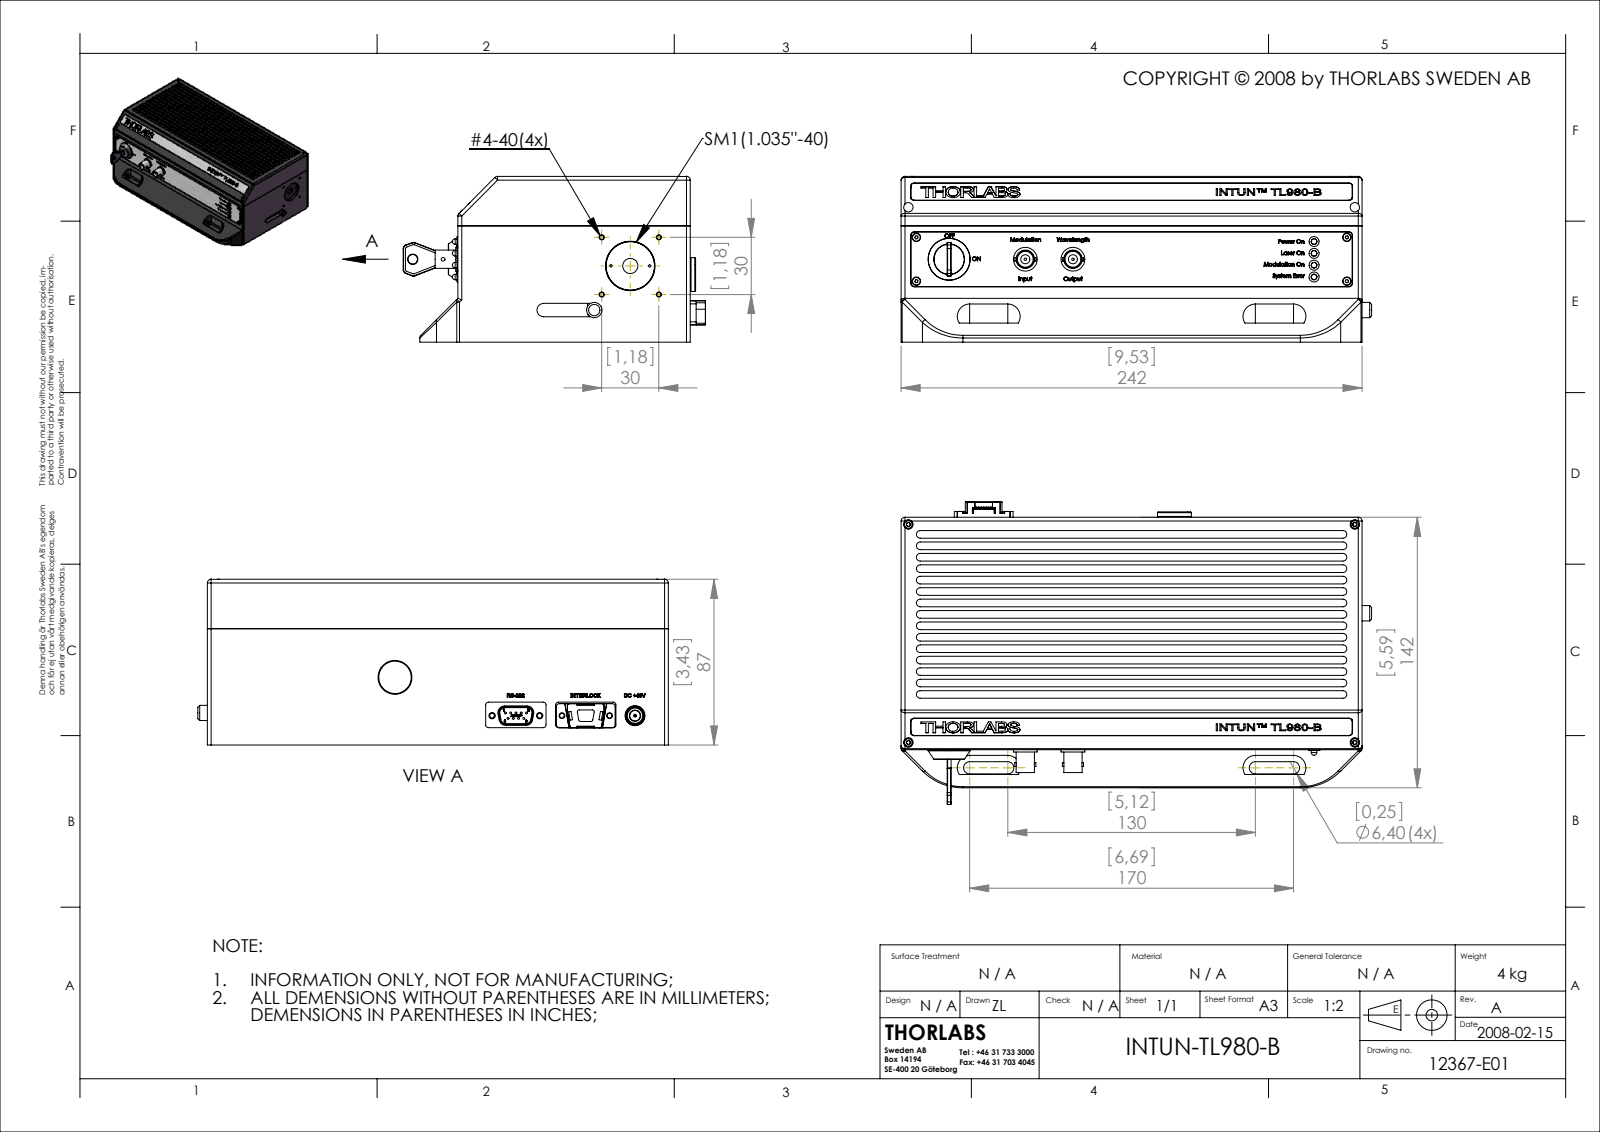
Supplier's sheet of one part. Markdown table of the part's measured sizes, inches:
| quantity | value |
| --- | --- |
| part name | INTUN-TL980-B |
| STEP written by | SolidWorks 2007 (CONFIG_CONTROL_DESIGN) |
| units | inches |
| bodies | 0 solids, 3236 faces (1794 planar, 636 cylindrical, 806 other) |
| overall size | 9.724 × 6.247 × 3.425 |
| round holes (diameter × count) | 0.04 × 9, 0.081 × 8, 0.063 × 4, 0.089 × 4, 0.094 × 4, 0.098 × 4, 0.114 × 4, 0.118 × 4, 0.12 × 4, 0.169 × 4, 0.177 × 4, 0.193 × 4 |
| round bosses / shafts (diameter × count) | 0.04 × 9, 0.177 × 5, 0.098 × 5, 0.244 × 4, 0.209 × 4, 0.185 × 4, 0.167 × 4, 0.157 × 4 |
| partial cylindrical surfaces (radius × count) | 0.079 × 68, 0.062 × 16, 0.008 × 14, 0.197 × 14, 0.138 × 10, 0.236 × 10, 0.028 × 9, 0.037 × 9 |
| main face-to-face distances | 0.236, 0.22, 0.246, 3.061, 2.841, 4.567, 0.079, 0.039, 3.268, 0.207 |
| hole center spacings | 0.109, 0.906, 0.62, 0.835, 1.153, 1.181, 0.124, 0.198 |
